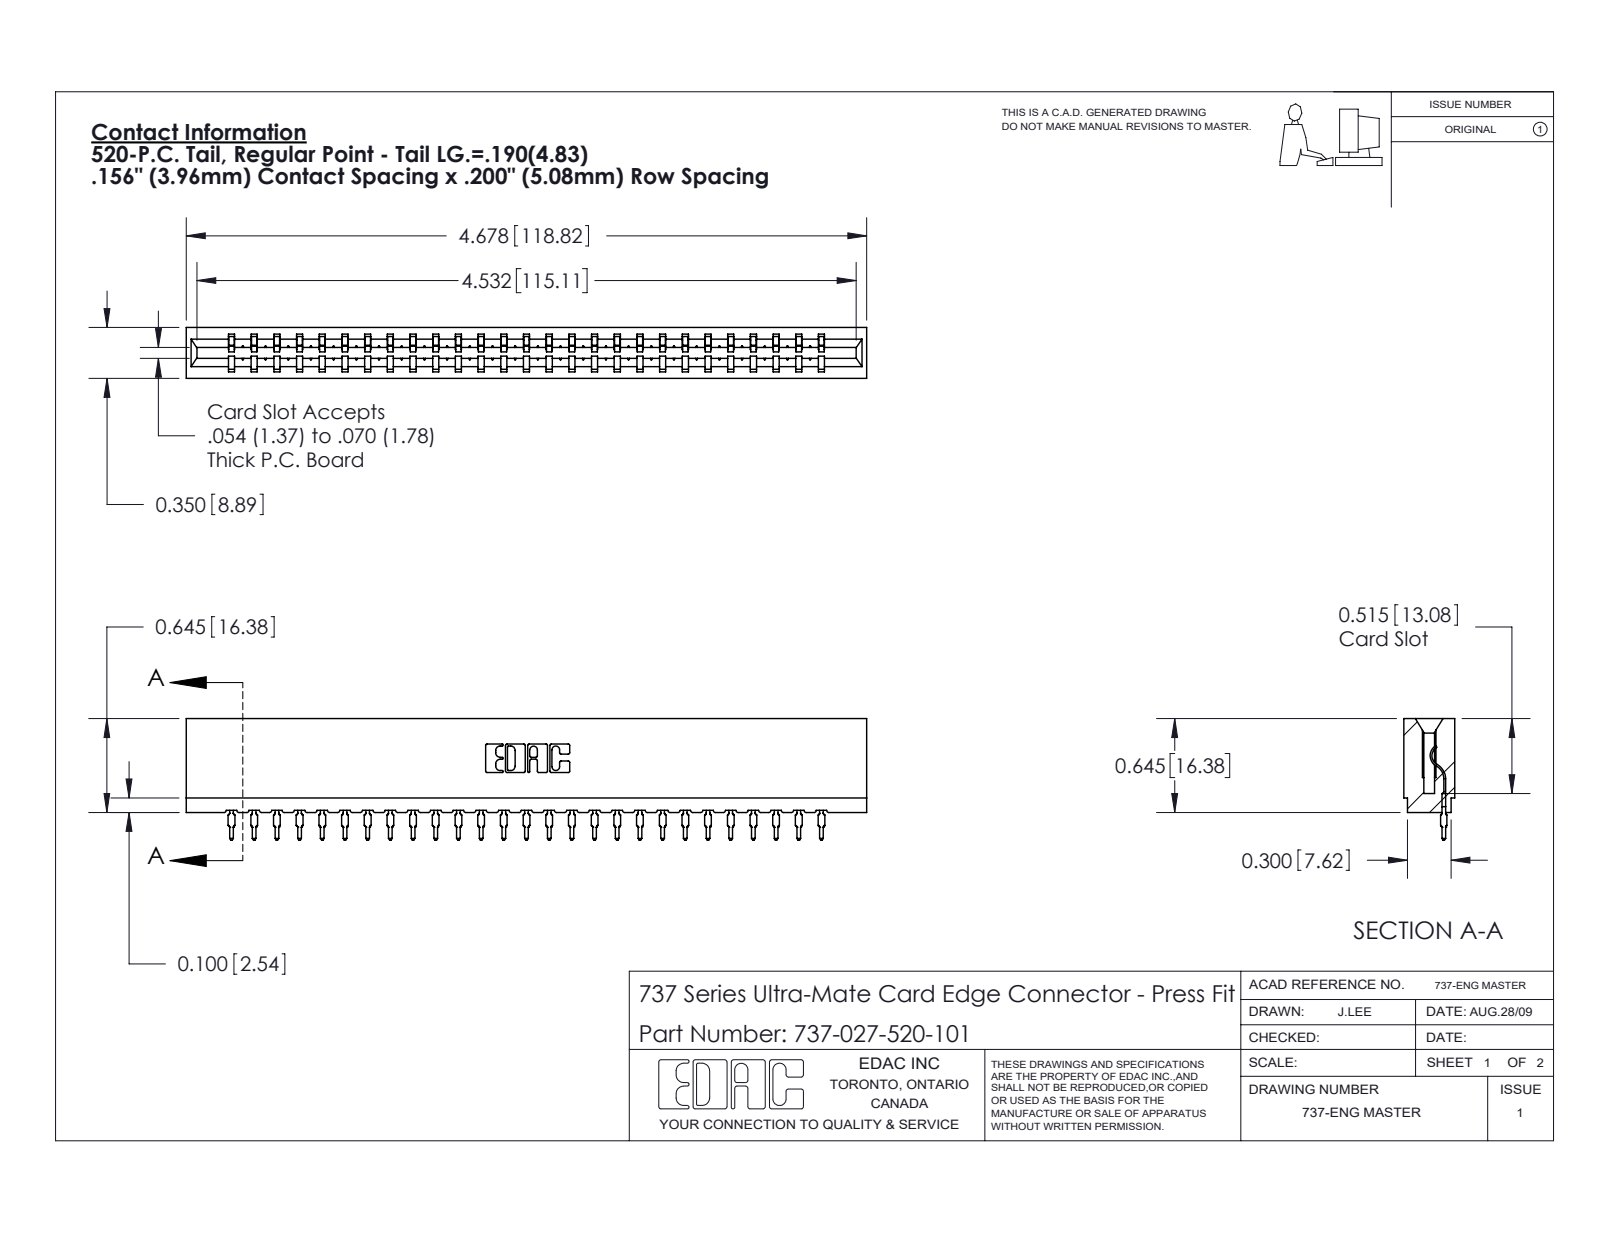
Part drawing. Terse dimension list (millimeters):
name: 737-027-520-101; 745-292-001_520; 737 Part_Insulator Option - 01
written by: SolidWorks 2020 (CONFIG_CONTROL_DESIGN)
unit: mm
bodies: 28 solids, 3145 faces (1890 planar, 553 cylindrical, 702 other)
size: 118.8 × 21.2 × 8.9
volume: 11 600 mm³; area: 15 060 mm²
rounds: 54× R0.4, 54× R0.5, 22× R0.3, 6× R0.2, 6× R0.8, 4× R0.1, 4× R0.3, 3× R0.7
face distances: 3.5, 5.4, 8.9, 15.8, 4, 1.9, 19.8, 1.1, 7.7, 2.4
